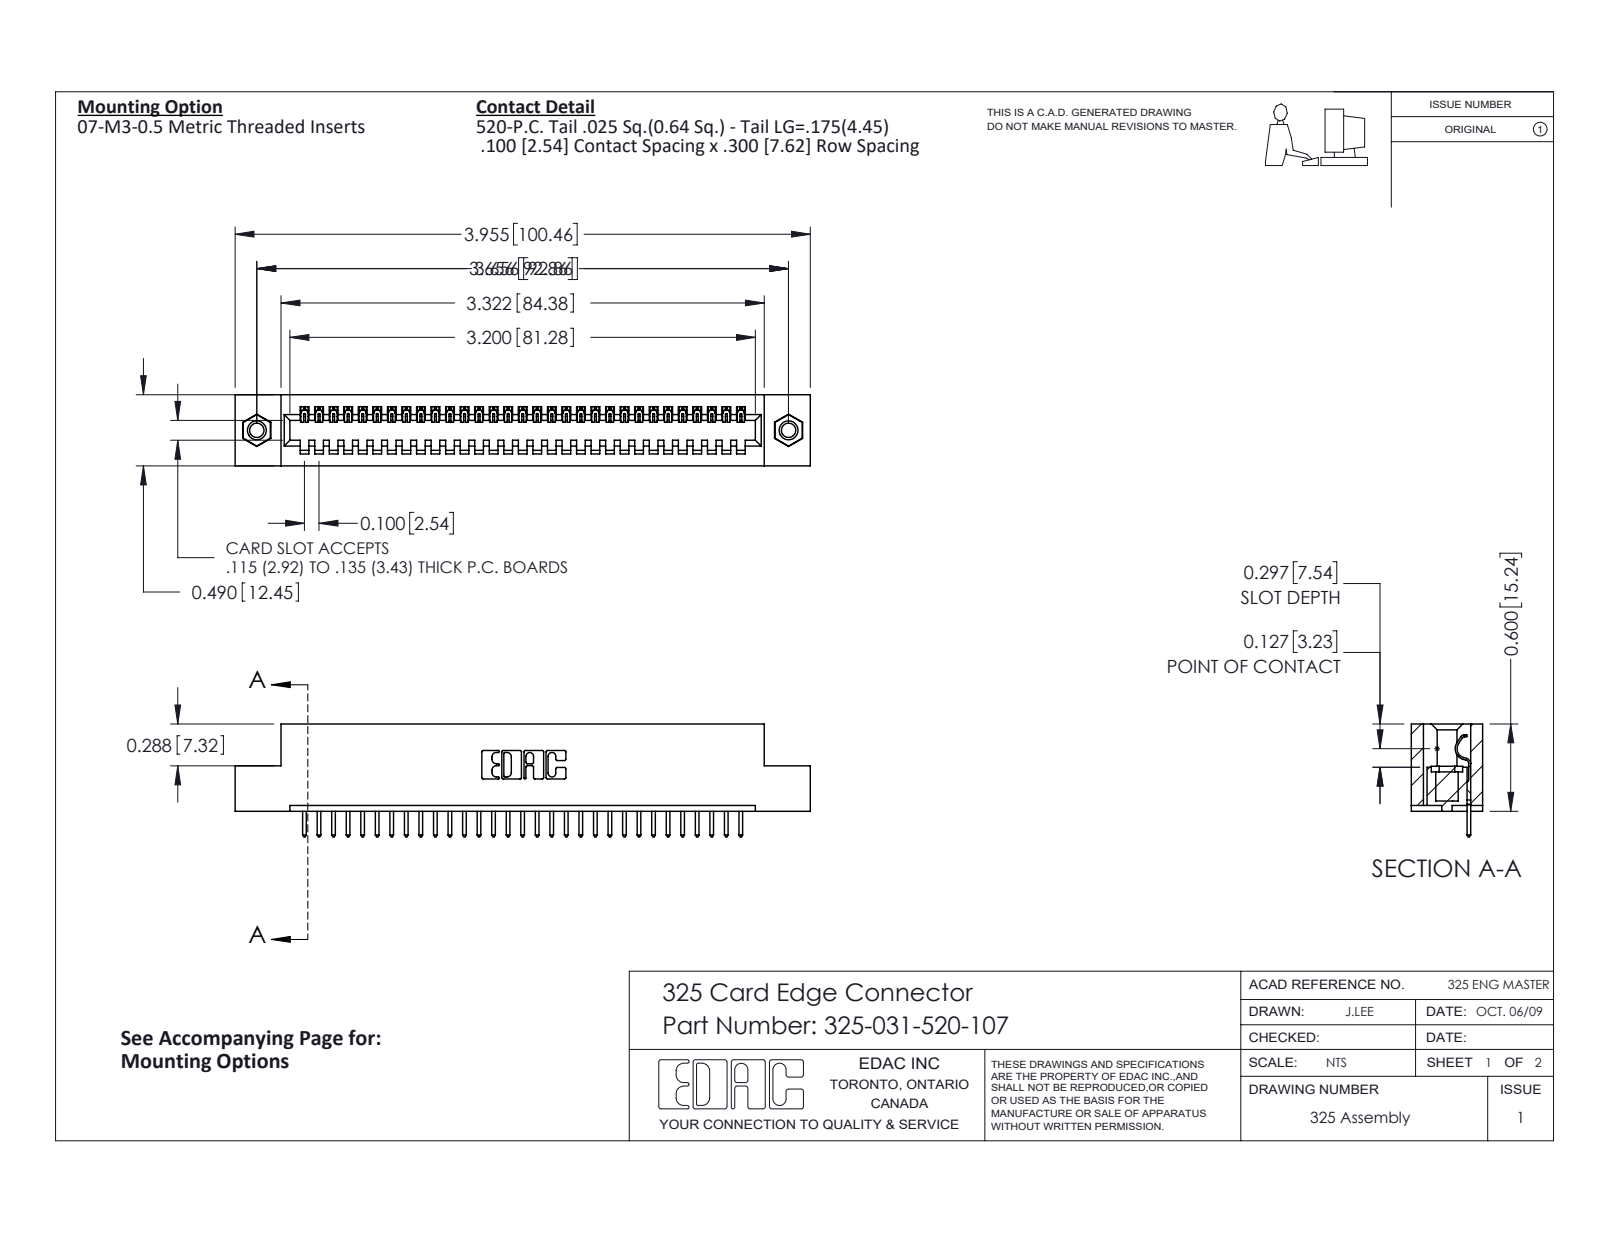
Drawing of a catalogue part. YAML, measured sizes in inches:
part_name: "325-292-001_325-293-120; 345-250-001_345-250-005-103; 325 Part_TI; 325-031-520-107"
step_written_by: "SolidWorks 2016 (CONFIG_CONTROL_DESIGN)"
units: inches
bodies: {solids: 34, faces: 1972, planar: 1404, cylindrical: 552, other: 16}
overall_size: [3.955, 0.775, 0.49]
volume: 0.767
surface_area: 20.54
round_holes:
  - {diameter: 0.098, count: 2}
  - {diameter: 0.125, count: 2}
  - {diameter: 0.16, count: 2}
round_bosses_or_shafts:
  - {diameter: 0.155, count: 2}
partial_cylinders:
  - {radius: 0.006, count: 62}
  - {radius: 0.01, count: 62}
  - {radius: 0.01, count: 22}
  - {radius: 0.007, count: 6}
  - {radius: 0.031, count: 6}
  - {radius: 0.026, count: 3}
  - {radius: 0.014, count: 1}
  - {radius: 0.022, count: 1}
face_to_face_distances: [0.083, 0.407, 0.49, 0.3, 0.107, 0.383, 0.025, 0.325, 0.04, 0.1]
hole_center_spacings: [3.656]
